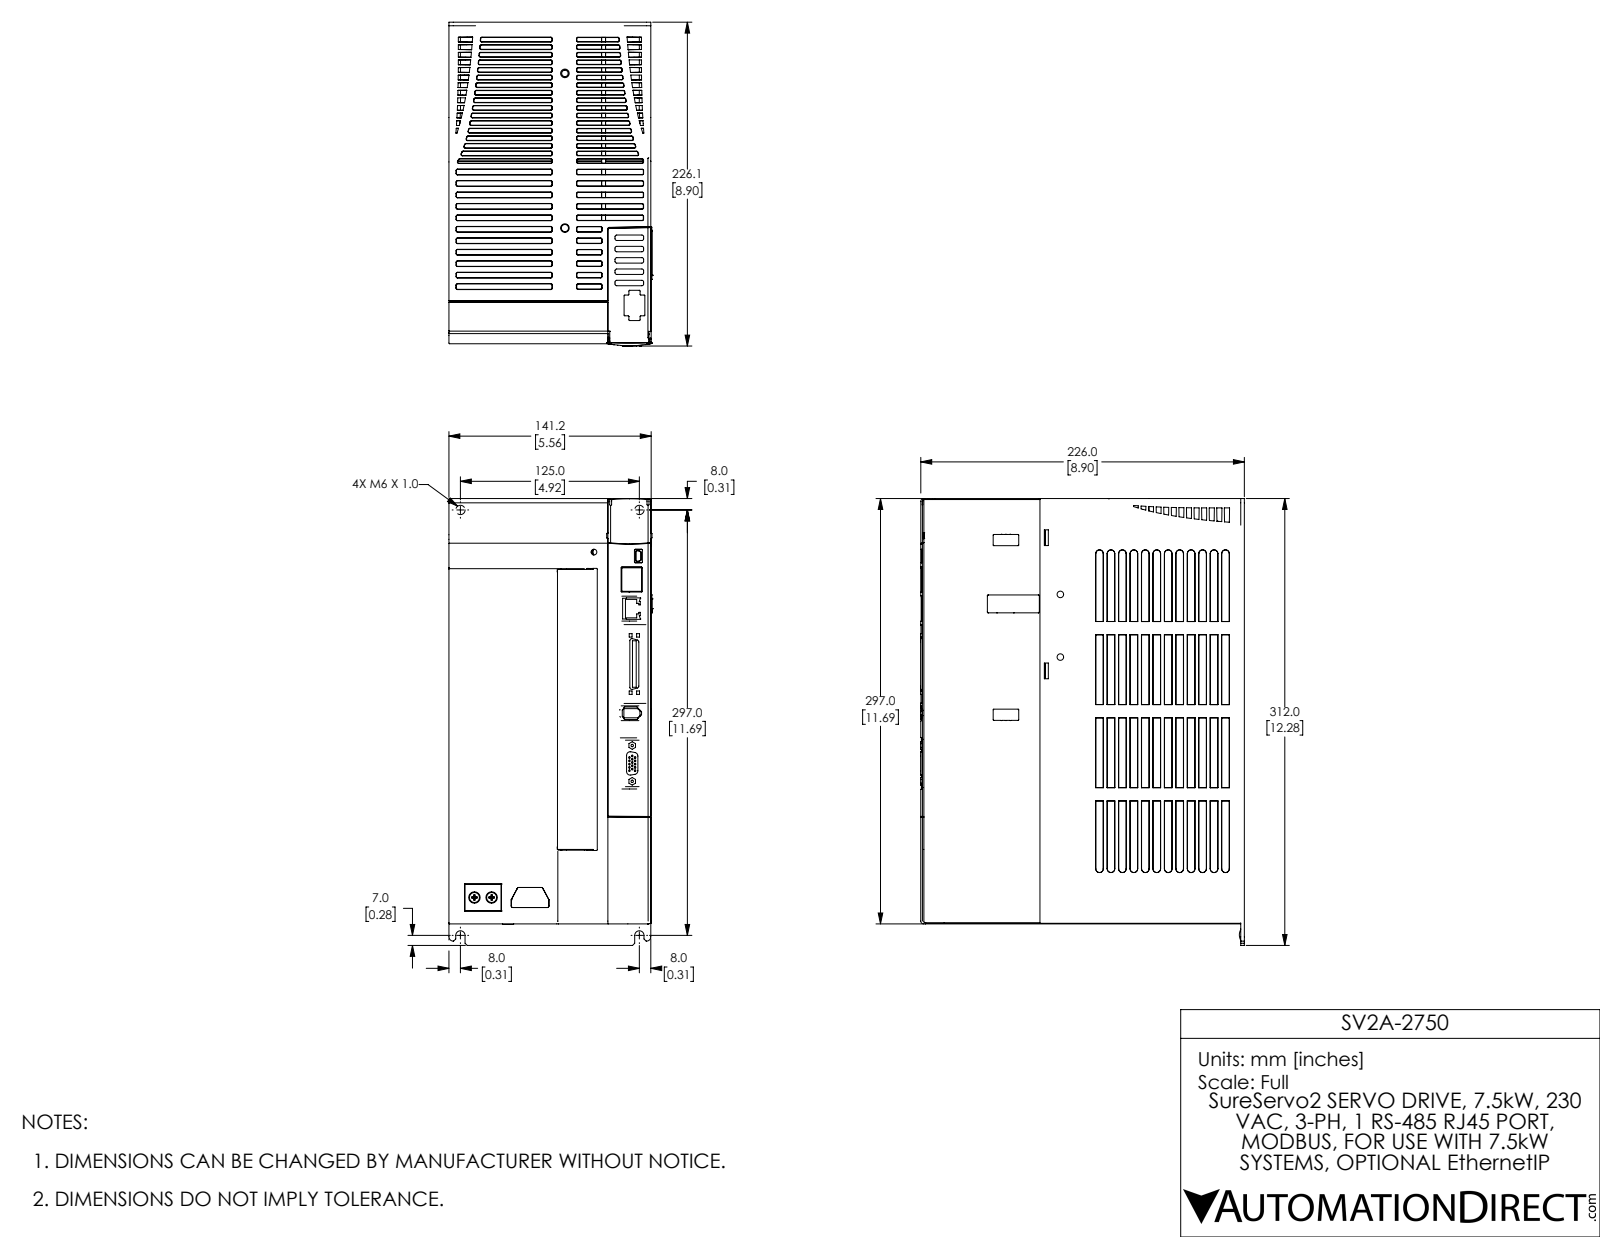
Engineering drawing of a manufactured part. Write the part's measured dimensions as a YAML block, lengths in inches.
part_name: "SV2A-4750_3D_All_20200930 1st B3c Extcoord NEW2C"
step_written_by: "SolidWorks 2017 (AUTOMOTIVE_DESIGN)"
units: inches
bodies: {solids: 4, faces: 3969, planar: 2159, cylindrical: 644, other: 1166}
overall_size: [12.283, 8.902, 5.591]
volume: 548.8
surface_area: 599.8
round_holes:
  - {diameter: 0.044, count: 15}
  - {diameter: 0.181, count: 4}
  - {diameter: 0.067, count: 2}
  - {diameter: 0.114, count: 2}
  - {diameter: 0.118, count: 2}
  - {diameter: 0.236, count: 2}
  - {diameter: 0.256, count: 2}
round_bosses_or_shafts:
  - {diameter: 0.315, count: 2}
  - {diameter: 0.276, count: 2}
  - {diameter: 0.256, count: 2}
  - {diameter: 0.157, count: 2}
  - {diameter: 0.024, count: 1}
partial_cylinders:
  - {radius: 0.02, count: 91}
  - {radius: 0.012, count: 90}
  - {radius: 0.004, count: 33}
  - {radius: 0.039, count: 16}
  - {radius: 0.098, count: 11}
  - {radius: 0.197, count: 11}
  - {radius: 0.008, count: 10}
  - {radius: 0.059, count: 10}
face_to_face_distances: [5.551, 0.02, 5.561, 5.541, 0.079, 8.276, 0.029, 11.664, 11.693, 0.089]
hole_center_spacings: [0.09, 0.156, 0.238, 0.09, 0.18, 0.18, 0.156, 0.27]
